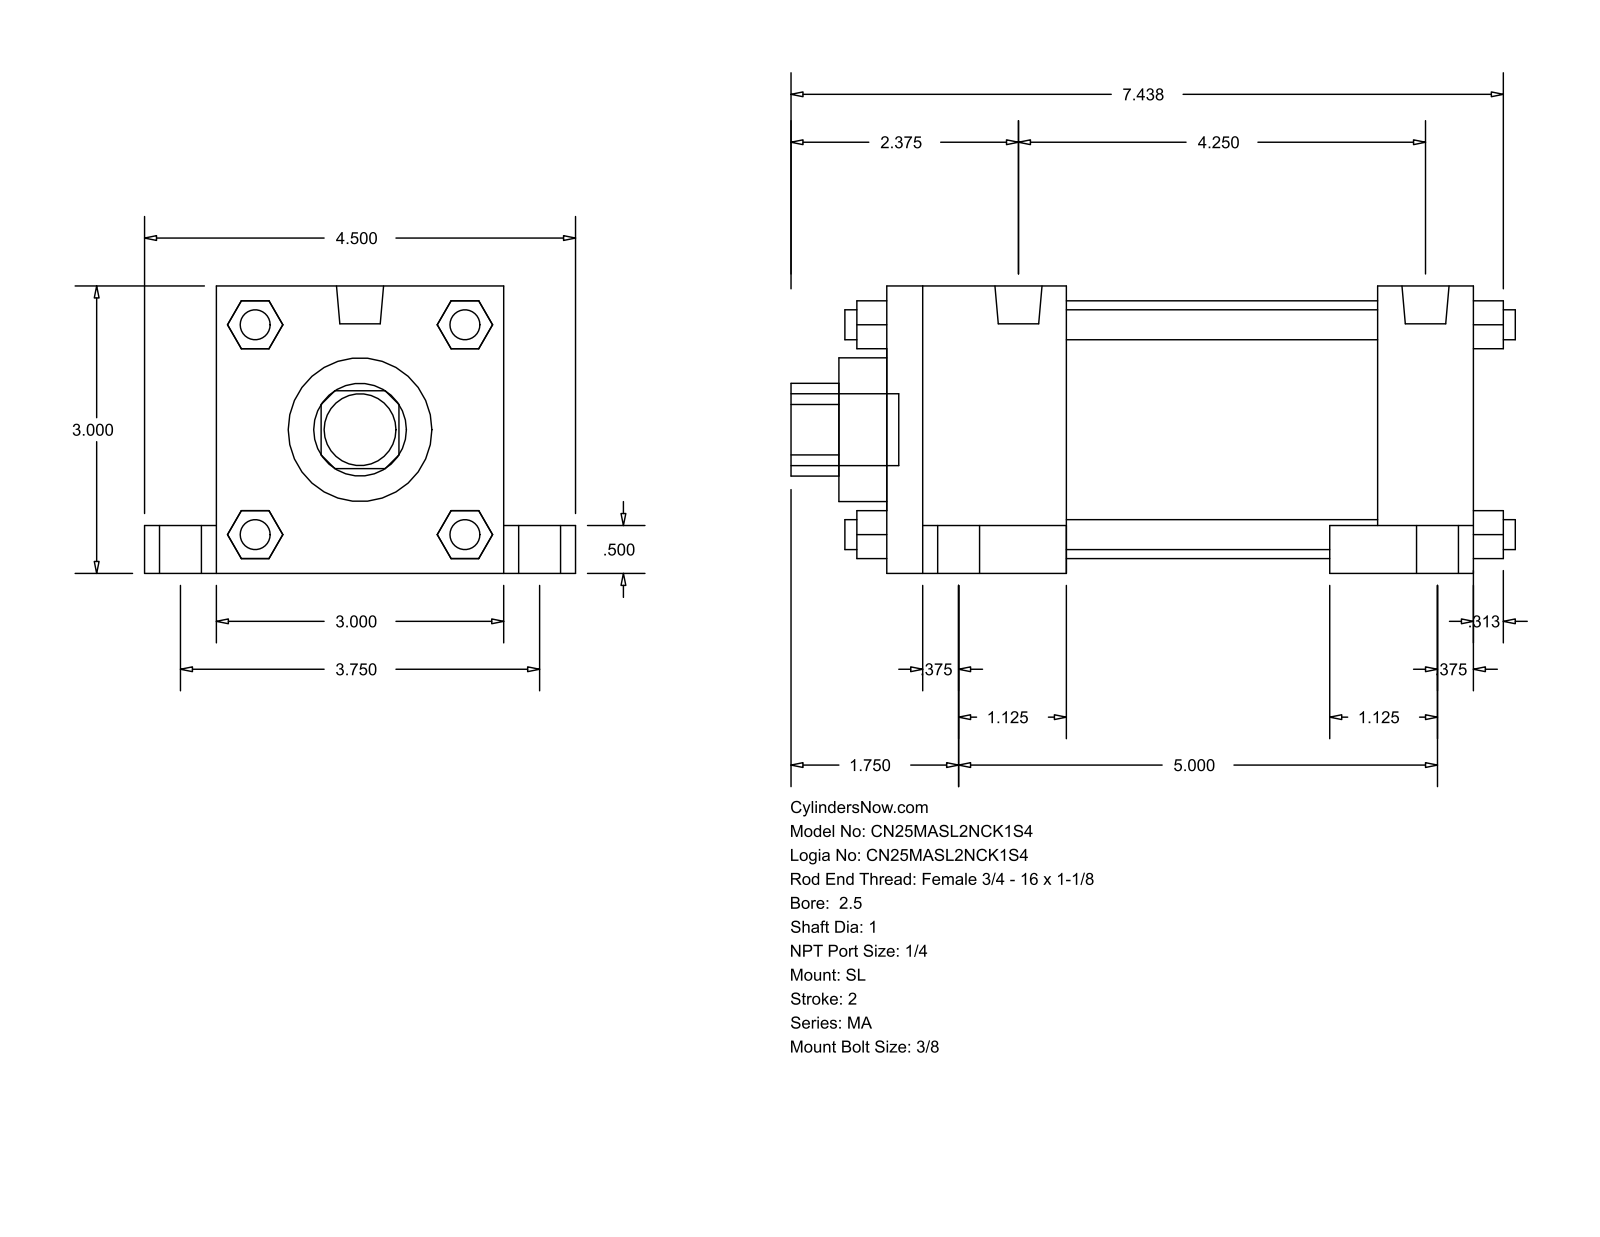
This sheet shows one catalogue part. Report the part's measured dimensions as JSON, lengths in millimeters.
{"part_name": "MA_SL__0250_1", "step_written_by": "GSSL Pune (CONFIG_CONTROL_DESIGN)", "units": "millimeters", "bodies": {"solids": 0, "faces": 148, "planar": 112, "cylindrical": 36, "other": 0}, "overall_size": [192.09, 114.3, 76.2], "round_holes": [[25.4, 1], [38.1, 1], [68.33, 1]], "round_bosses_or_shafts": [[7.94, 8], [17.46, 4], [11.11, 4], [12.49, 2], [19.05, 1]], "partial_cylinders_radius": [[12.29, 1]], "face_to_face_distances": [76.2, 155.57, 12.7, 25.4, 47.63, 107.94, 130.17, 82.54, 19.05, 95.25]}
